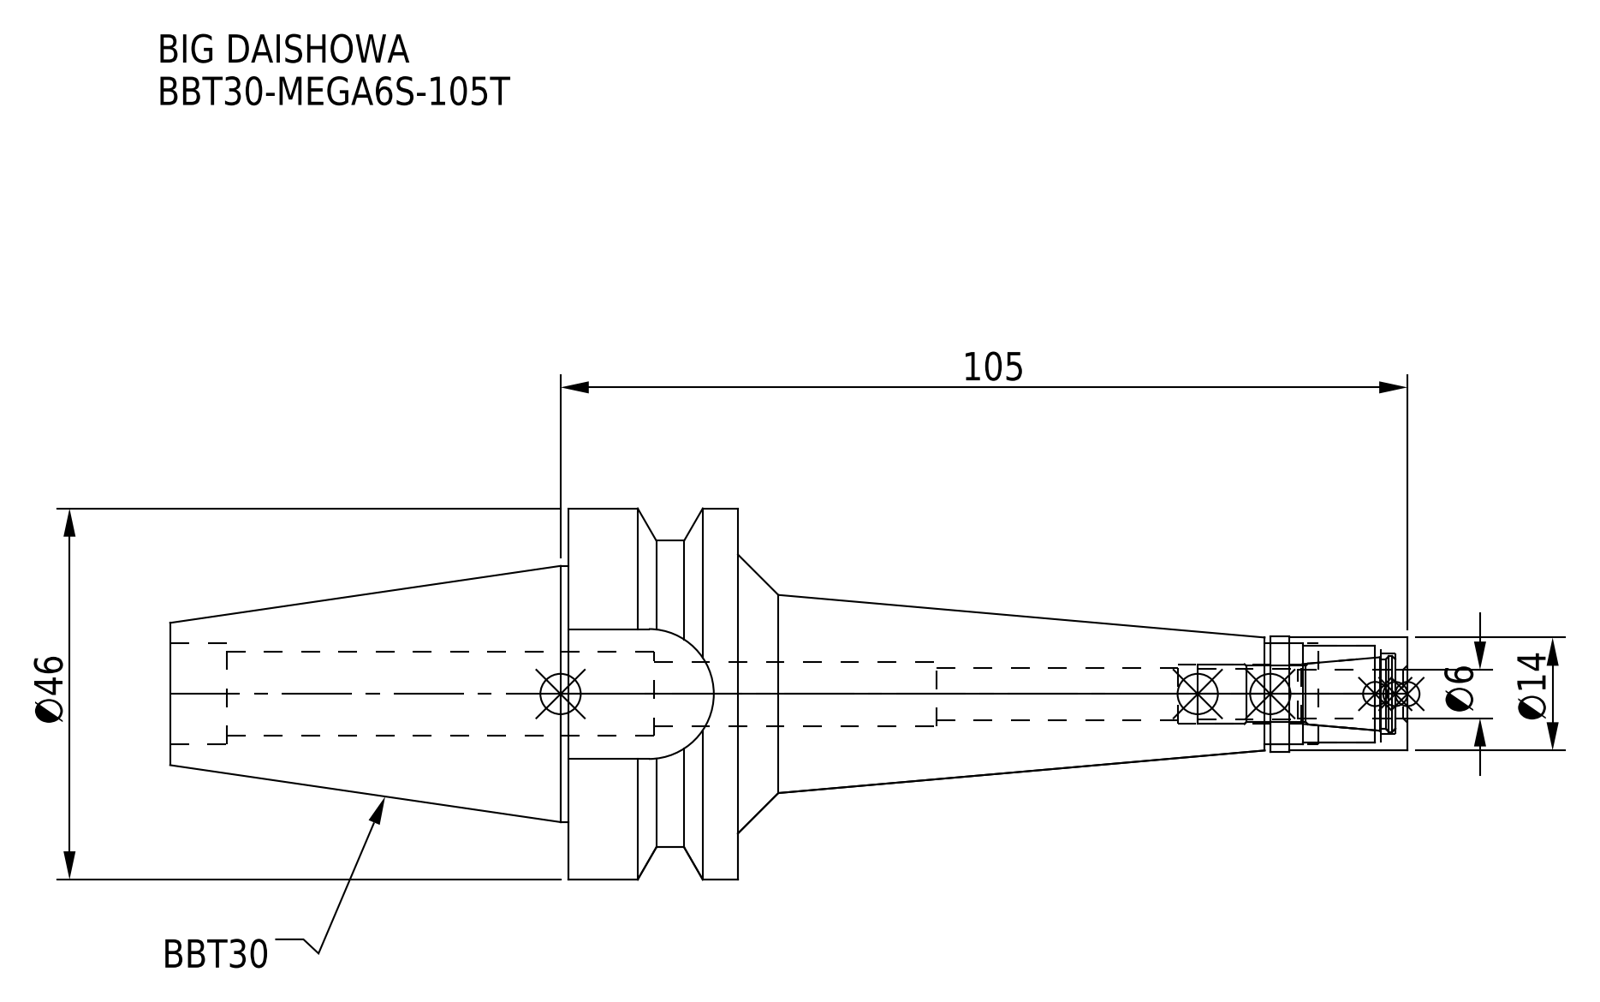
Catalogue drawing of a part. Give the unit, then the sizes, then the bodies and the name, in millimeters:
Units: millimetres
Overall size (bounding box): 153.4 × 46 × 46
Round holes (diameter × count): ⌀6.1 ×1, ⌀6.4 ×1, ⌀7.4 ×1, ⌀8 ×1, ⌀10 ×1, ⌀10.4 ×1, ⌀12 ×1, ⌀12.5 ×1
Round bosses / shafts (diameter × count): ⌀46 ×1, ⌀31.75 ×1, ⌀14.3 ×1, ⌀14 ×1
Partial cylindrical surfaces — rounded edges, fillets, slot ends (radius × count): R8.05 ×1, R19 ×1
Main face-to-face distances: 21, 32.6, 70.4, 49.4, 83, 104, 153.4, 16.1, 0.7, 13.7
Volume: 68 532 mm³ · Surface area: 19 906 mm²
Bodies: 2 solids, 74 faces (22 planar, 38 cylindrical, 14 other)
Part name (STEP PRODUCT): DXF_TEMP_ASSY_ASM_4_ASM.stp; MGN6S_1.stp; BBT30-MEGA6S-105T.stp; BBT30MS06105T-060_ASM.stp (+3 more)
STEP written by: SolidWorks 2019 (CONFIG_CONTROL_DESIGN)
